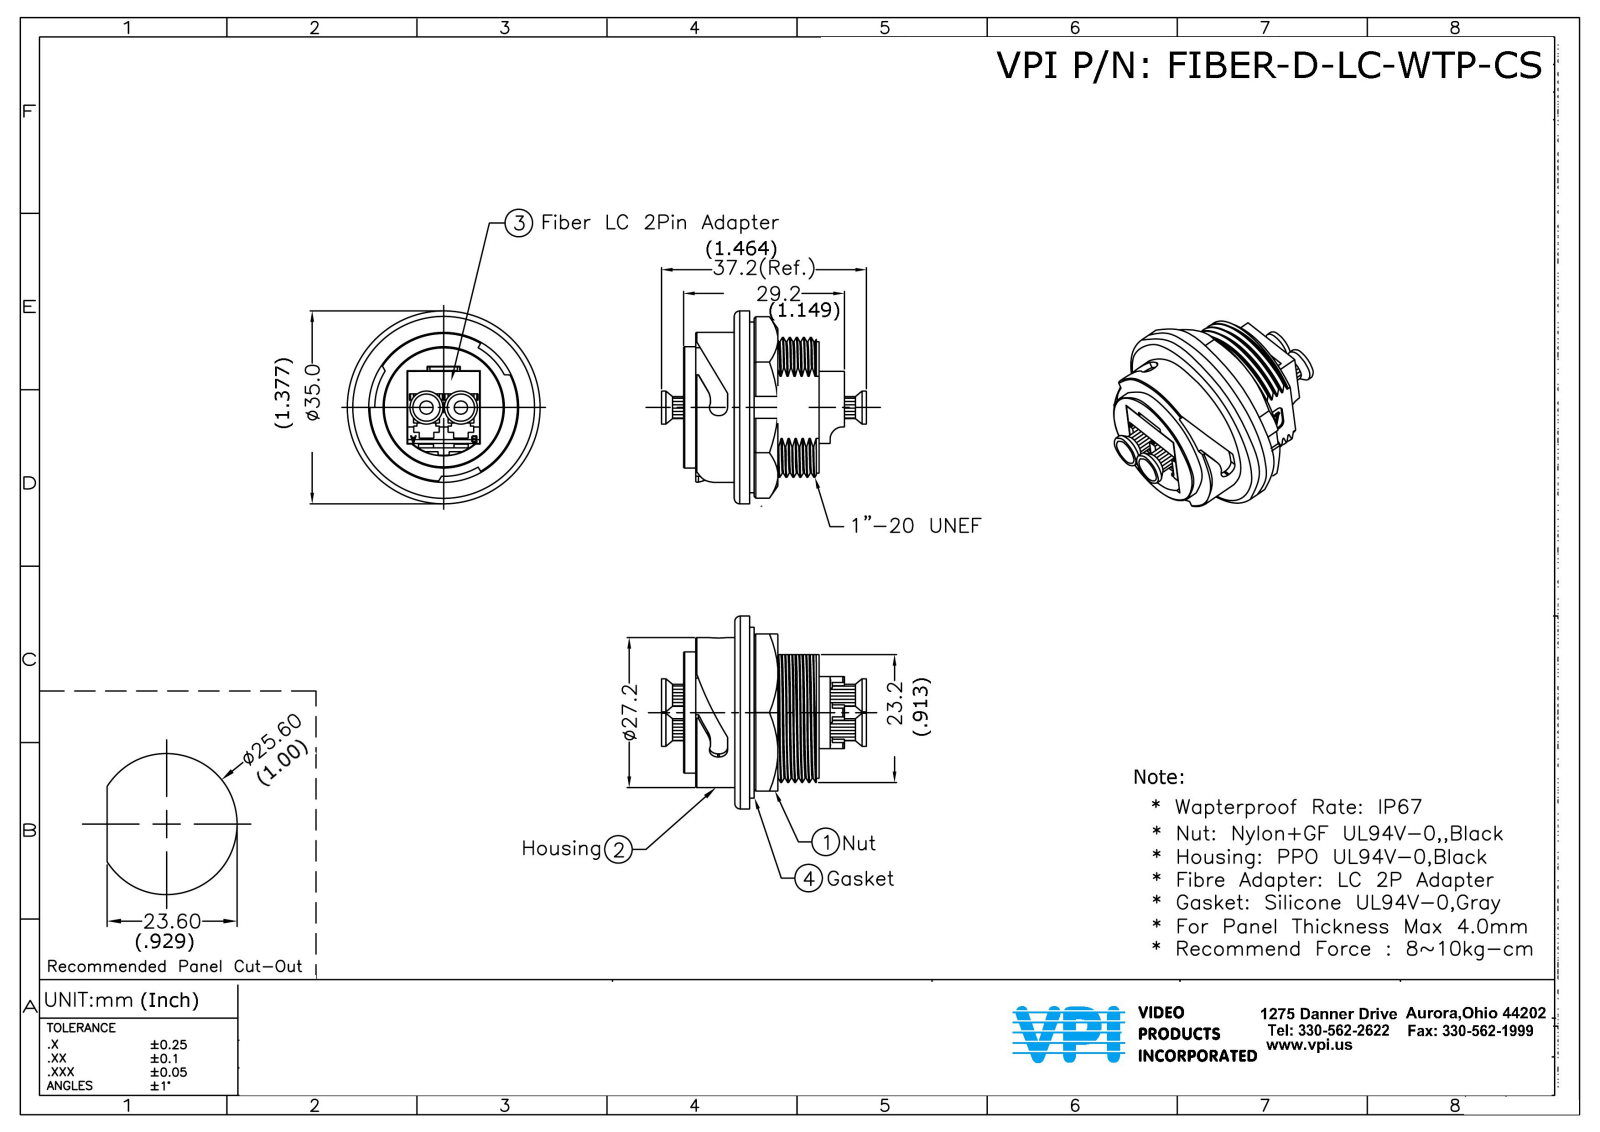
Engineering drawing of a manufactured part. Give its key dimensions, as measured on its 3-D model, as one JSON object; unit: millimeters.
{"part_name": "FIBER-D-LC-WTP-CS", "step_written_by": "SolidWorks 2011 (AUTOMOTIVE_DESIGN)", "units": "millimeters", "bodies": {"solids": 8, "faces": 507, "planar": 317, "cylindrical": 100, "other": 90}, "overall_size": [37.2, 35, 35], "volume_mm3": 12901, "surface_area_mm2": 12238, "round_holes": [[1.25, 2], [24.05, 1], [25.2, 1]], "round_bosses_or_shafts": [[6, 2], [4, 2], [2.92, 2], [35, 1], [31, 1], [27.2, 1], [25.4, 1], [23.84, 1]], "partial_cylinders_radius": [[0.5, 4], [1.99, 2], [1.99, 2], [2.3, 2], [2.6, 1], [12.5, 1]], "face_to_face_distances": [13.08, 0.85, 3.65, 4.7, 2.8, 14.18, 5.76, 7.32, 1.06, 12.02], "hole_center_spacings": [3.13, 6.26]}
